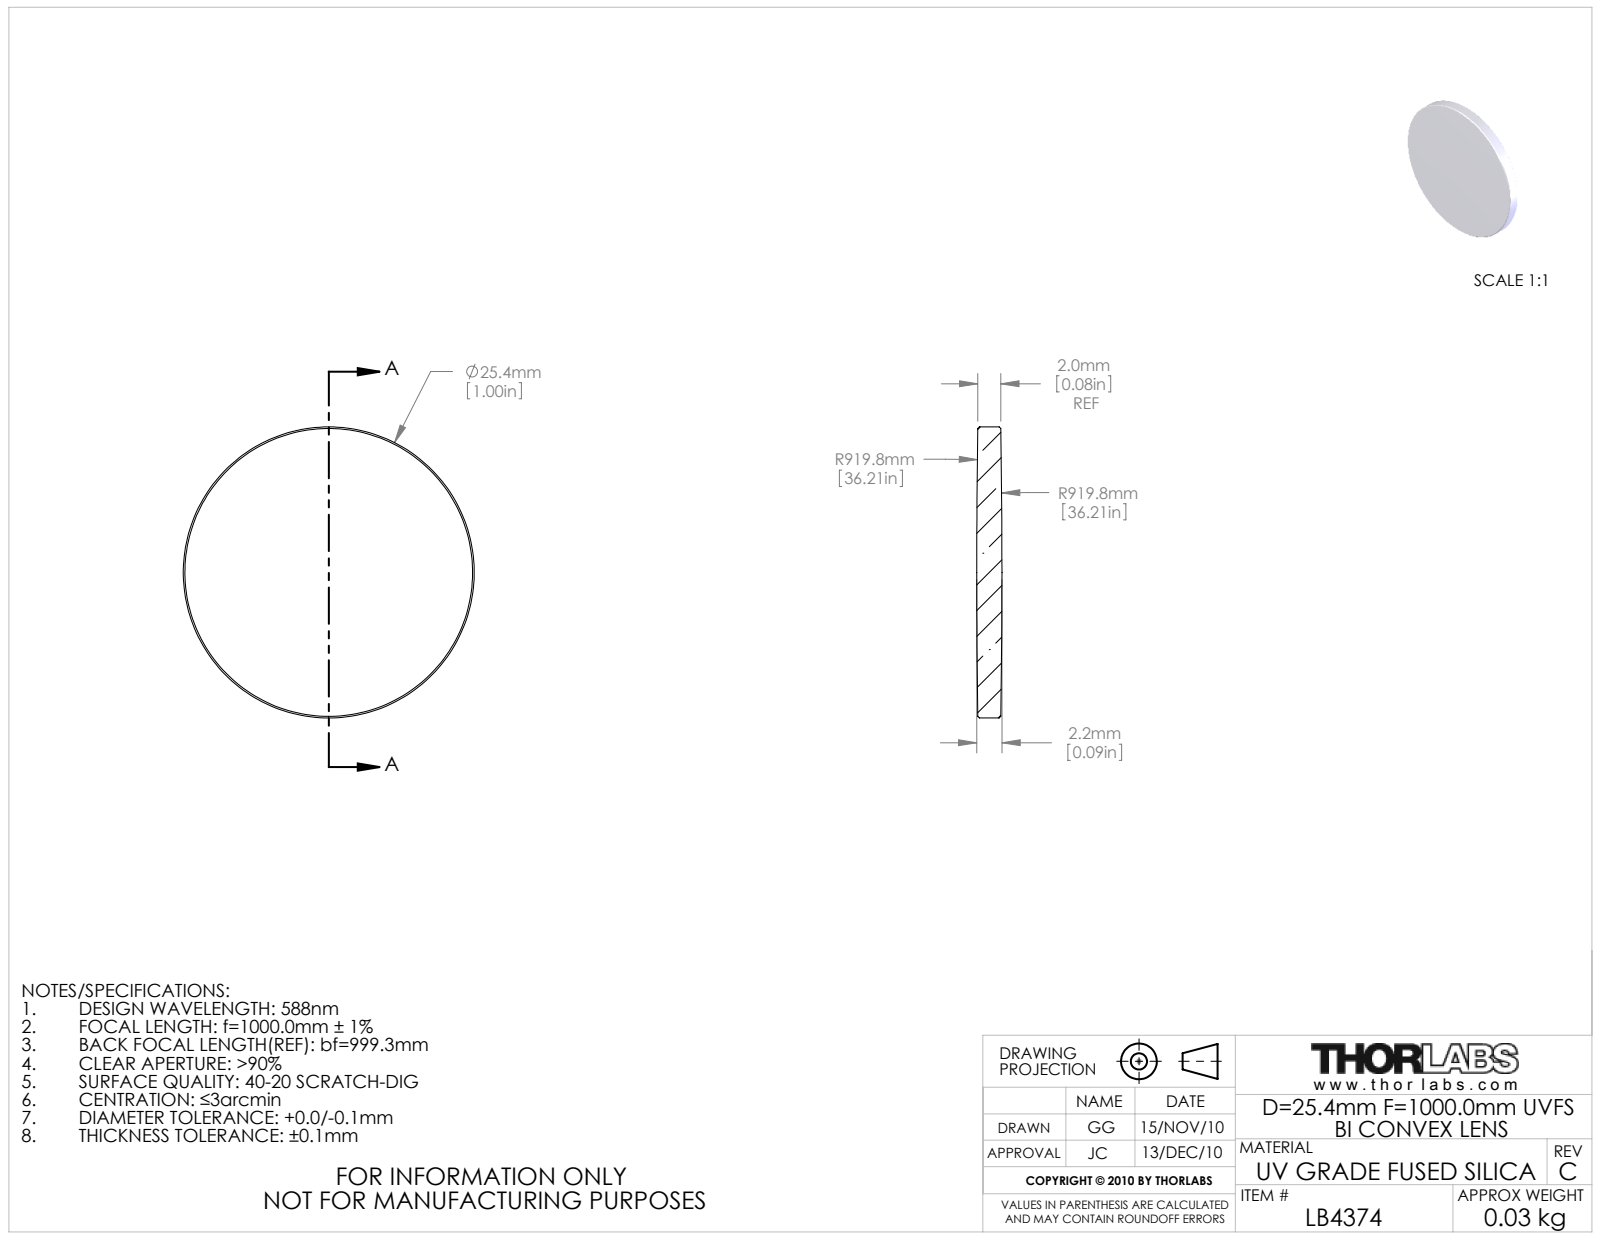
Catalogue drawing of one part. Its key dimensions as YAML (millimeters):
part_name: "3412-E0W"
step_written_by: "SolidWorks 2009 (AUTOMOTIVE_DESIGN)"
units: millimeters
bodies: {solids: 1, faces: 10, planar: 0, cylindrical: 2, other: 8}
overall_size: [25.4, 25.4, 2.2]
volume: 1060
surface_area: 1160
round_bosses_or_shafts:
  - {diameter: 25.4, count: 1}
